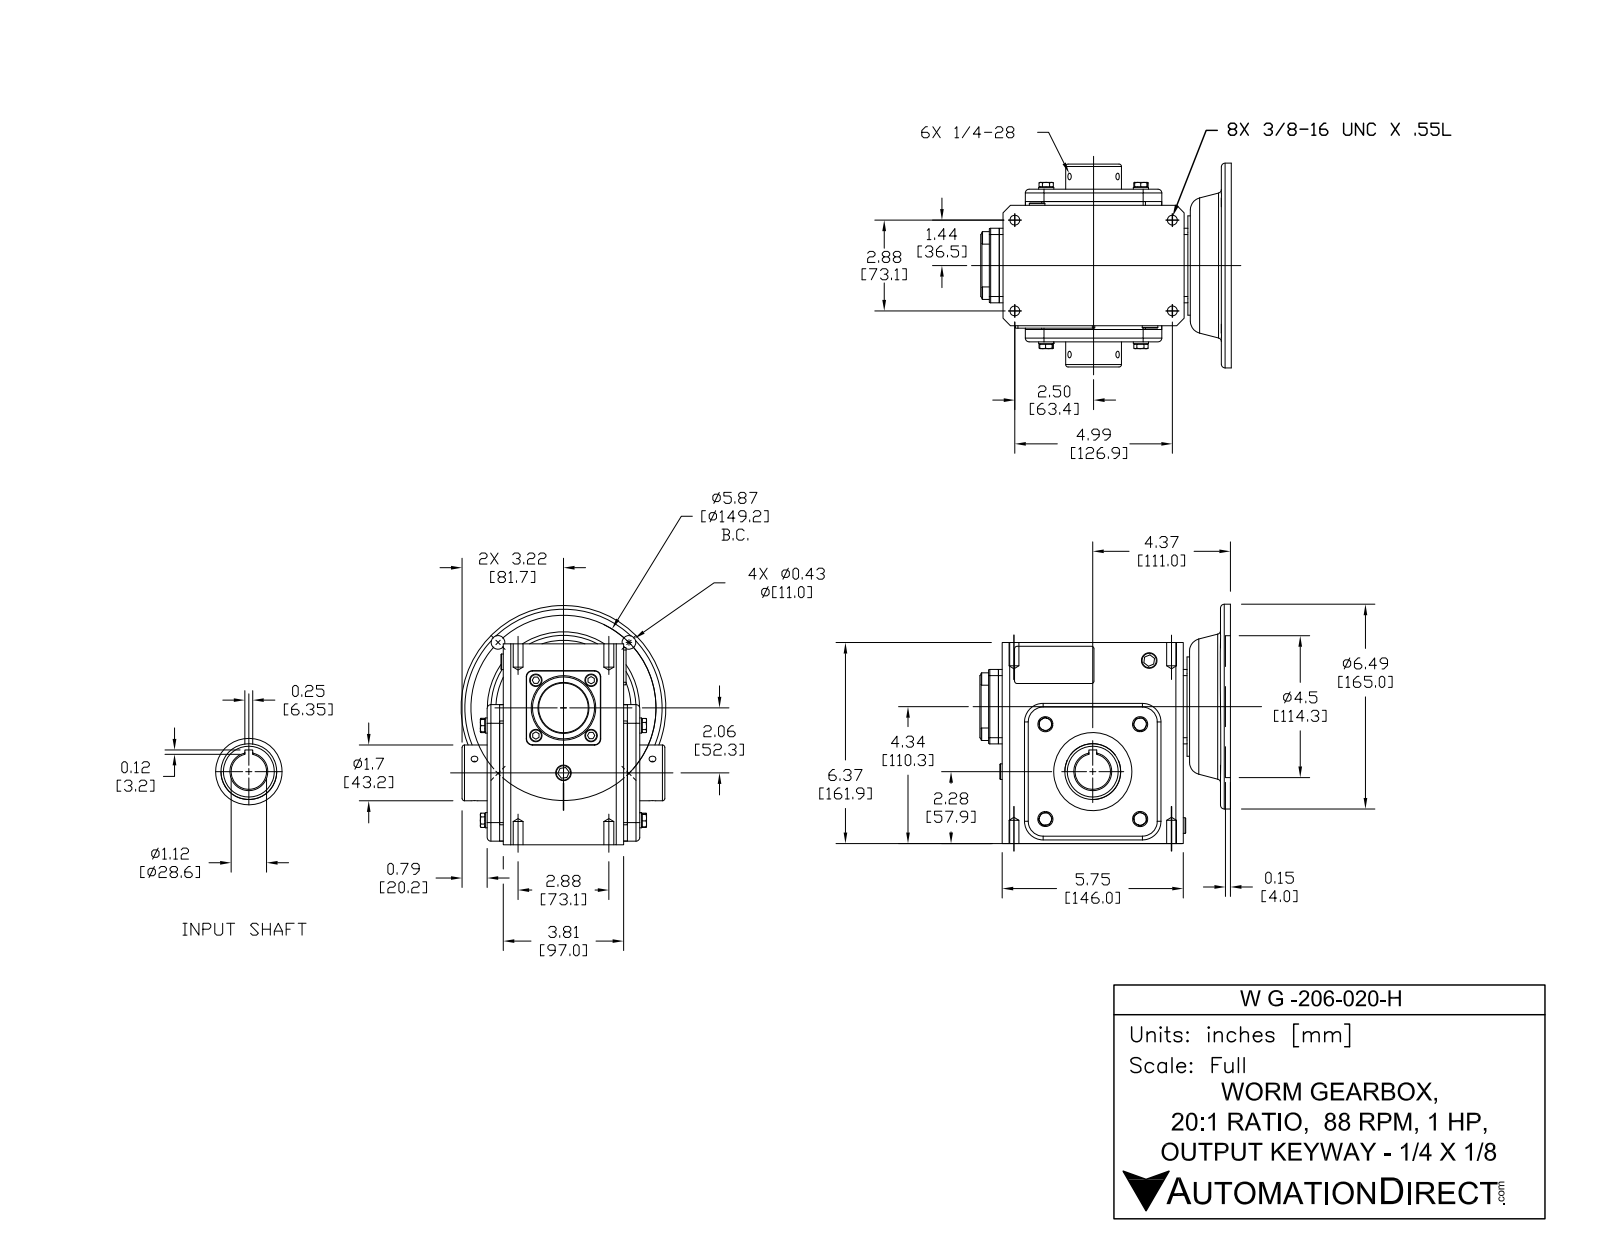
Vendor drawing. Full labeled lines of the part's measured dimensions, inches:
Part name (STEP PRODUCT): WG-206-040-H
STEP written by: SolidWorks 2015 (CONFIG_CONTROL_DESIGN)
Units: inches
Bodies: 45 solids, 628 faces (304 planar, 198 cylindrical, 126 other)
Overall size (bounding box): 7.953 × 7.591 × 6.496
Volume: 171 in³ · Surface area: 463.1 in²
Round holes (diameter × count): ⌀0.213 ×6, ⌀0.313 ×4, ⌀0.406 ×4, ⌀0.591 ×1, ⌀0.625 ×1, ⌀1.125 ×1, ⌀1.457 ×1, ⌀1.772 ×1, ⌀2.402 ×1, ⌀3.543 ×1, ⌀4.5 ×1
Round bosses / shafts (diameter × count): ⌀0.394 ×8, ⌀0.48 ×4, ⌀6.496 ×1, ⌀3.15 ×1, ⌀2.047 ×1, ⌀1.575 ×1, ⌀1.181 ×1, ⌀1.142 ×1
Partial cylindrical surfaces — rounded edges, fillets, slot ends (radius × count): R0.079 ×8, R0.118 ×8, R0.197 ×4, R0.591 ×4, R0.02 ×2, R0.039 ×2, R2.717 ×1
Main face-to-face distances: 0.118, 4.055, 0.394, 4.331, 3.937, 0.512, 4.449, 6.375, 5.866, 1.181
Hole centre spacings: 2.858, 2.937, 4.154, 4.943, 5.65, 2.077, 2.88, 4.631
